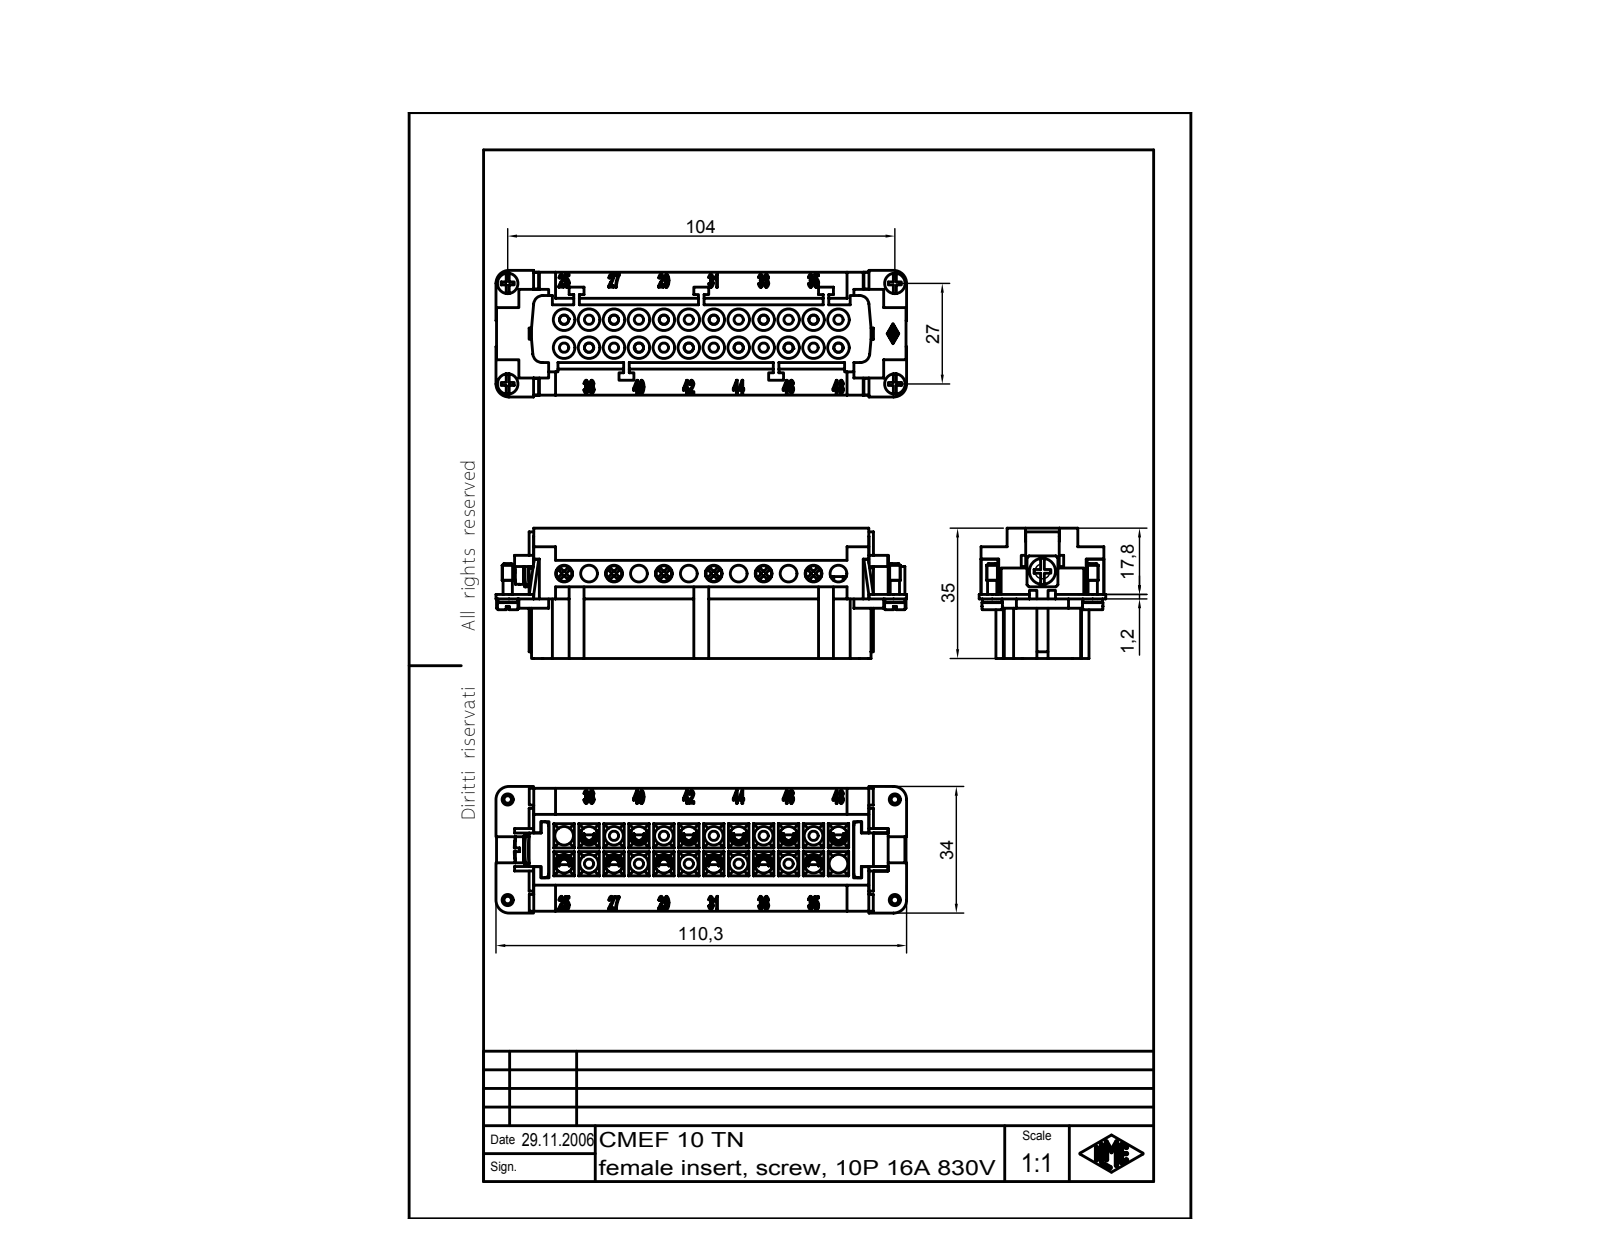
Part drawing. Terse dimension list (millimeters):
name: CMEF 10 TN
written by: Autodesk Inventor 7 (AUTOMOTIVE_DESIGN)
unit: mm
bodies: 25 solids, 2220 faces (1096 planar, 286 cylindrical, 838 other)
size: 110.3 × 35 × 34
volume: 53 425 mm³; area: 40 390 mm²
holes: 12× ⌀3, 12× ⌀4.5, 11× ⌀5, 2× ⌀2.55
bosses: 16× ⌀2.5, 12× ⌀4.2, 2× ⌀5.5, 2× ⌀5.3, 2× ⌀5, 2× ⌀3, 1× ⌀7
rounds: 14× R0.1, 12× R2.1, 4× R2.5, 2× R1, 2× R3.5, 1× R1.62, 1× R5.5
face distances: 1.75, 17.25, 19, 16, 15.5, 8.75, 3.25, 7, 24.25, 7.1
hole spacings: 13.4, 6.7, 26.8, 20.1, 40.2, 33.5, 10.06, 15.36
